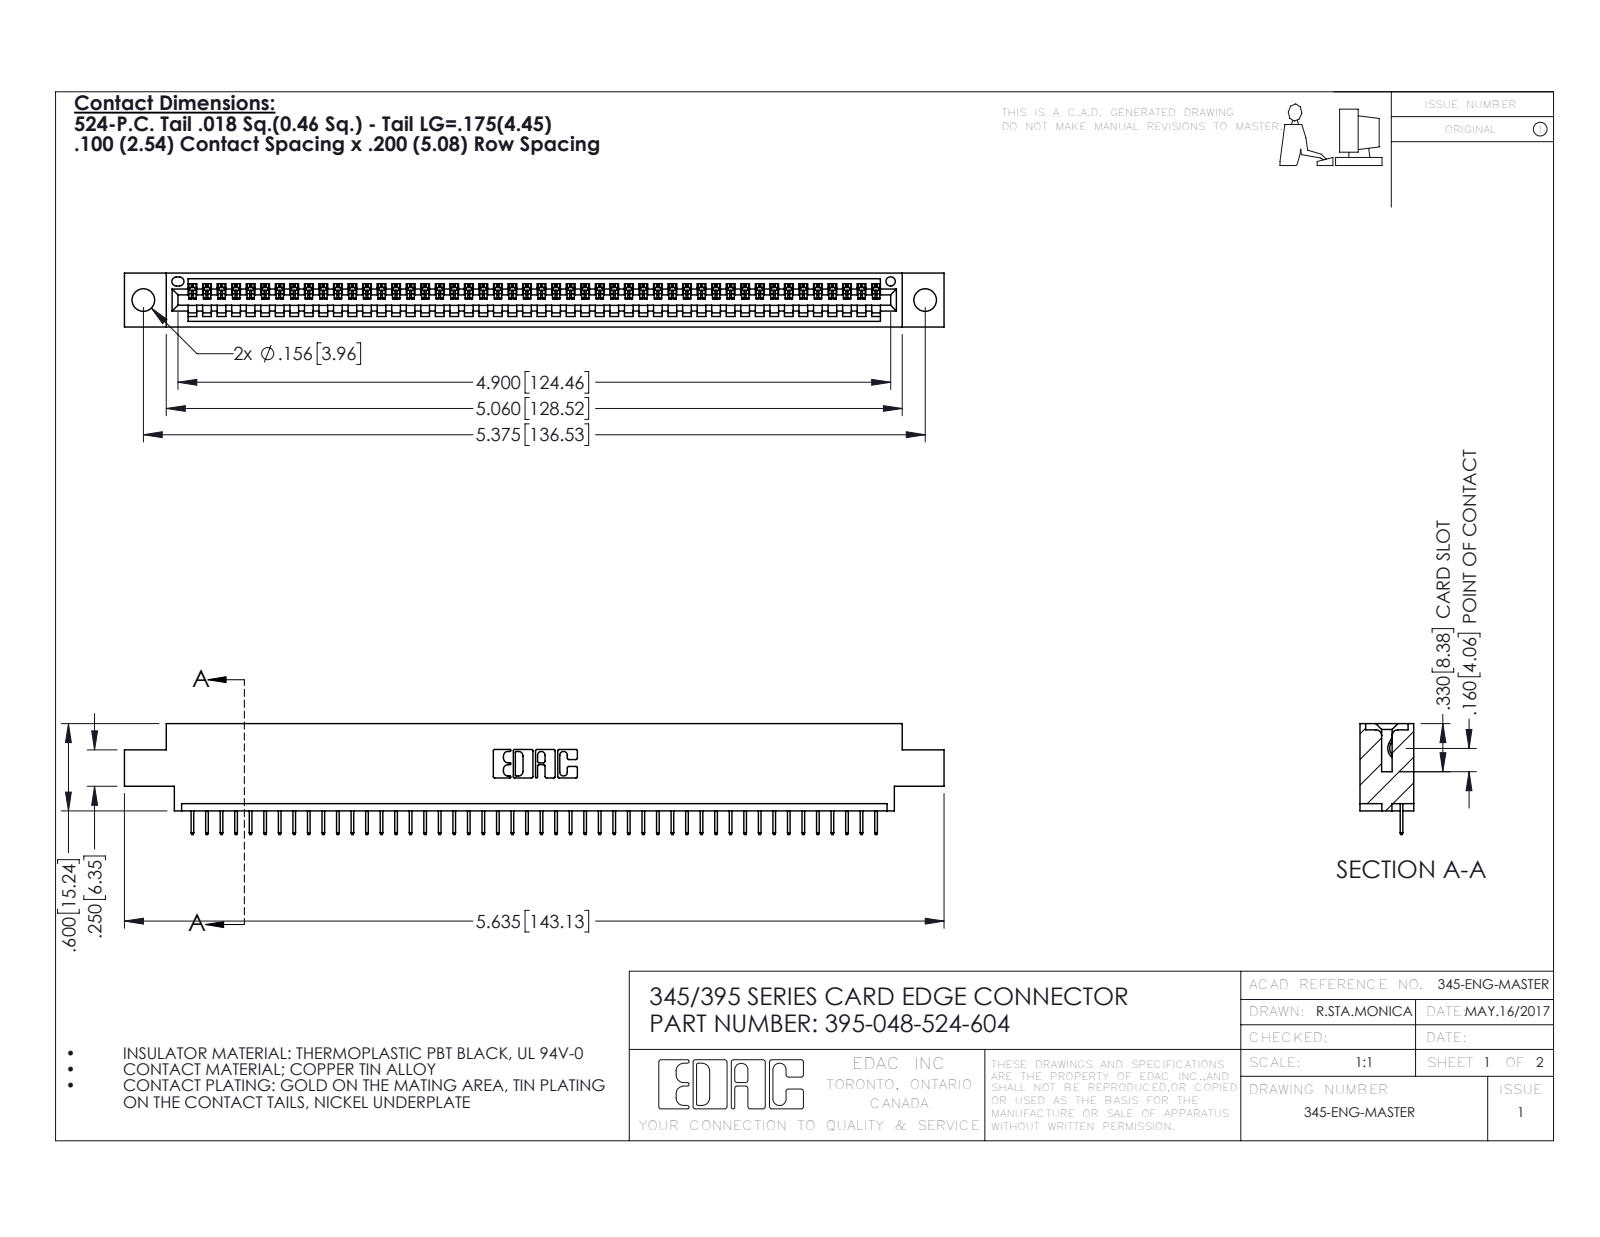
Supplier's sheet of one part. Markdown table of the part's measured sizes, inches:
| quantity | value |
| --- | --- |
| part name | 395-048-524-604; 345-292-001_345-293-124; 345 Part_0.170 Offset - 0.156 Dia-TH |
| STEP written by | SolidWorks 2016 (CONFIG_CONTROL_DESIGN) |
| units | inches |
| bodies | 49 solids, 3106 faces (2292 planar, 814 cylindrical, 0 other) |
| overall size | 5.635 × 0.762 × 0.37 |
| volume | 0.809 in³ |
| surface area | 26.38 in² |
| round holes (diameter × count) | 0.156 × 2, 0.064 × 1 |
| partial cylindrical surfaces (radius × count) | 0.006 × 96, 0.01 × 22, 0.007 × 6, 0.031 × 6, 0.026 × 3, 0.031 × 2, 0.04 × 2, 0.014 × 1 |
| main face-to-face distances | 0.072, 0.298, 0.37, 0.2, 0.098, 0.272, 0.025, 0.225, 0.072, 0.175 |
| hole center spacings | 0.27, 5.139, 5.375 |
